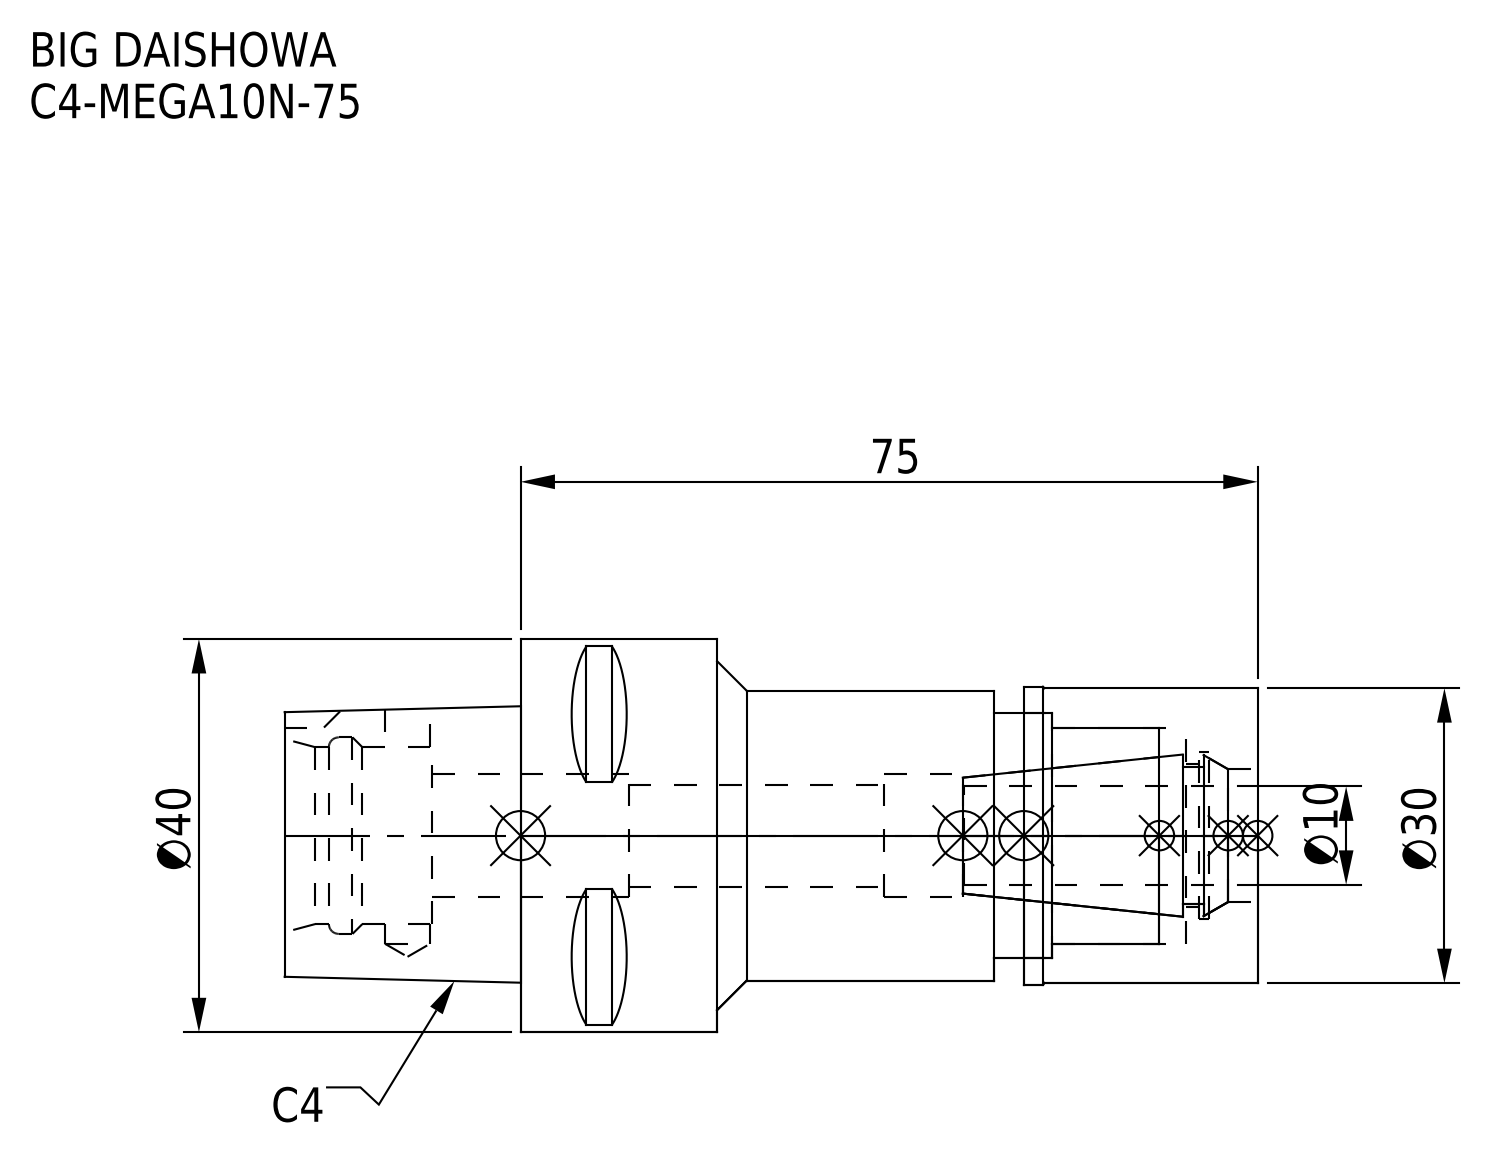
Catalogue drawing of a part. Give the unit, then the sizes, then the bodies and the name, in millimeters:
Units: millimetres
Overall size (bounding box): 99 × 40 × 40
Round holes (diameter × count): ⌀4.6 ×1, ⌀10.4 ×1, ⌀12.5 ×1, ⌀13.5 ×1, ⌀14.5 ×1, ⌀17 ×1, ⌀18 ×1, ⌀20 ×1, ⌀22 ×1, ⌀25 ×1
Round bosses / shafts (diameter × count): ⌀40 ×1, ⌀30.3 ×1, ⌀30 ×1, ⌀29.5 ×1
Partial cylindrical surfaces — rounded edges, fillets, slot ends (radius × count): R3 ×1
Main face-to-face distances: 75, 20, 55, 23.8, 31.2, 51.2, 20.9, 2.9, 34.1, 54.1
Volume: 61 670 mm³ · Surface area: 19 365 mm²
Bodies: 2 solids, 95 faces (38 planar, 39 cylindrical, 18 other)
Part name (STEP PRODUCT): DXF_TEMP_ASSY_ASM_4_ASM.stp; C4-MEGA10N-75-100_ASM.stp; MGN10_1.stp; C4-MEGA10N-75 (+3 more)
STEP written by: SolidWorks 2019 (CONFIG_CONTROL_DESIGN)
